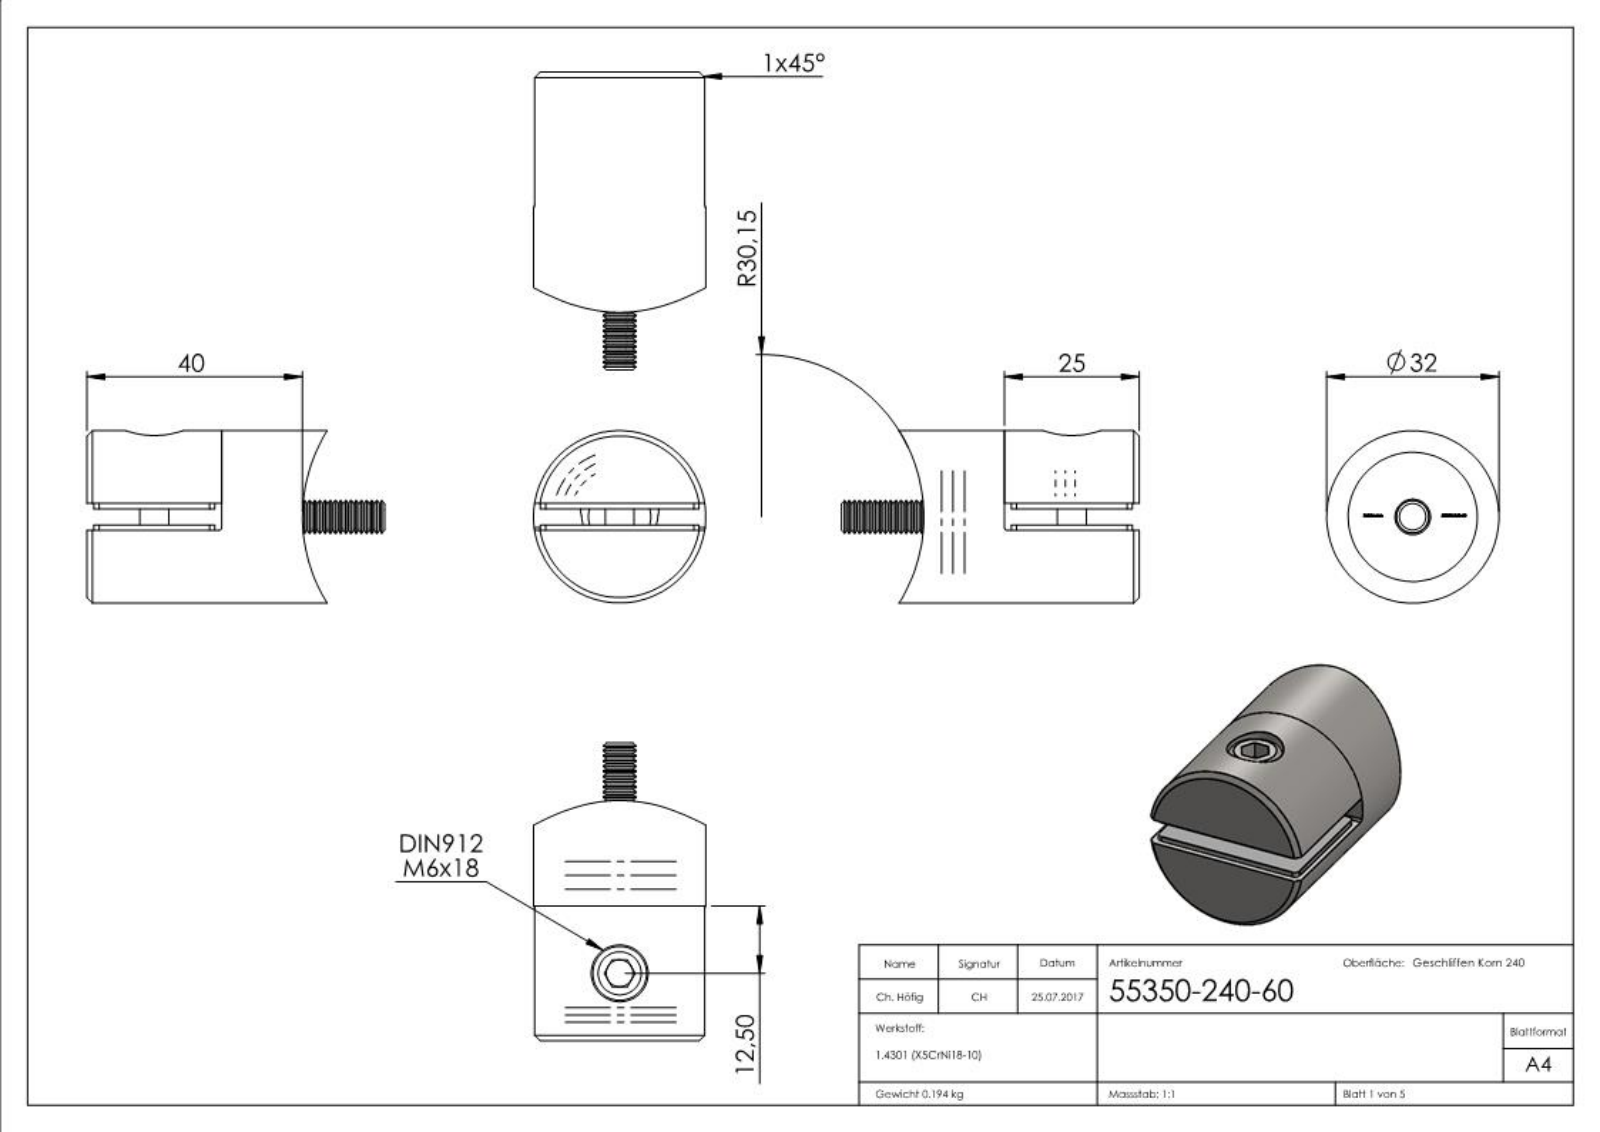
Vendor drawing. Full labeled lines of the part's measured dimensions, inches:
Part name (STEP PRODUCT): 5533X-240 Teil2; 5533X-240 Teil1_55350-240-60 Teil1; 55350-240-60; DIN 912 M6x18_DIN 912 M6x18 (+7 more)
STEP written by: SolidWorks 2018 (CONFIG_CONTROL_DESIGN)
Units: inches
Bodies: 6 solids, 432 faces (192 planar, 55 cylindrical, 185 other)
Overall size (bounding box): 2.176 × 1.26 × 1.26
Volume: 1.616 in³ · Surface area: 21.24 in²
Round holes (diameter × count): ⌀0.157 ×4, ⌀0.197 ×1, ⌀0.256 ×1, ⌀0.26 ×1, ⌀0.276 ×1, ⌀0.417 ×1, ⌀0.945 ×1
Round bosses / shafts (diameter × count): ⌀0.157 ×2, ⌀1.26 ×1, ⌀0.456 ×1, ⌀0.394 ×1, ⌀0.236 ×1, ⌀0.211 ×1
Partial cylindrical surfaces — rounded edges, fillets, slot ends (radius × count): R0.039 ×4, R0.02 ×1, R0.281 ×1, R0.287 ×1, R1.187 ×1
Main face-to-face distances: 0.157, 0.039, 0.197, 0.118, 0.984, 0.374, 1.358, 0.295, 0.413, 0.256
Hole centre spacings: 0.406, 0.412, 0.522, 0.512, 0.531
